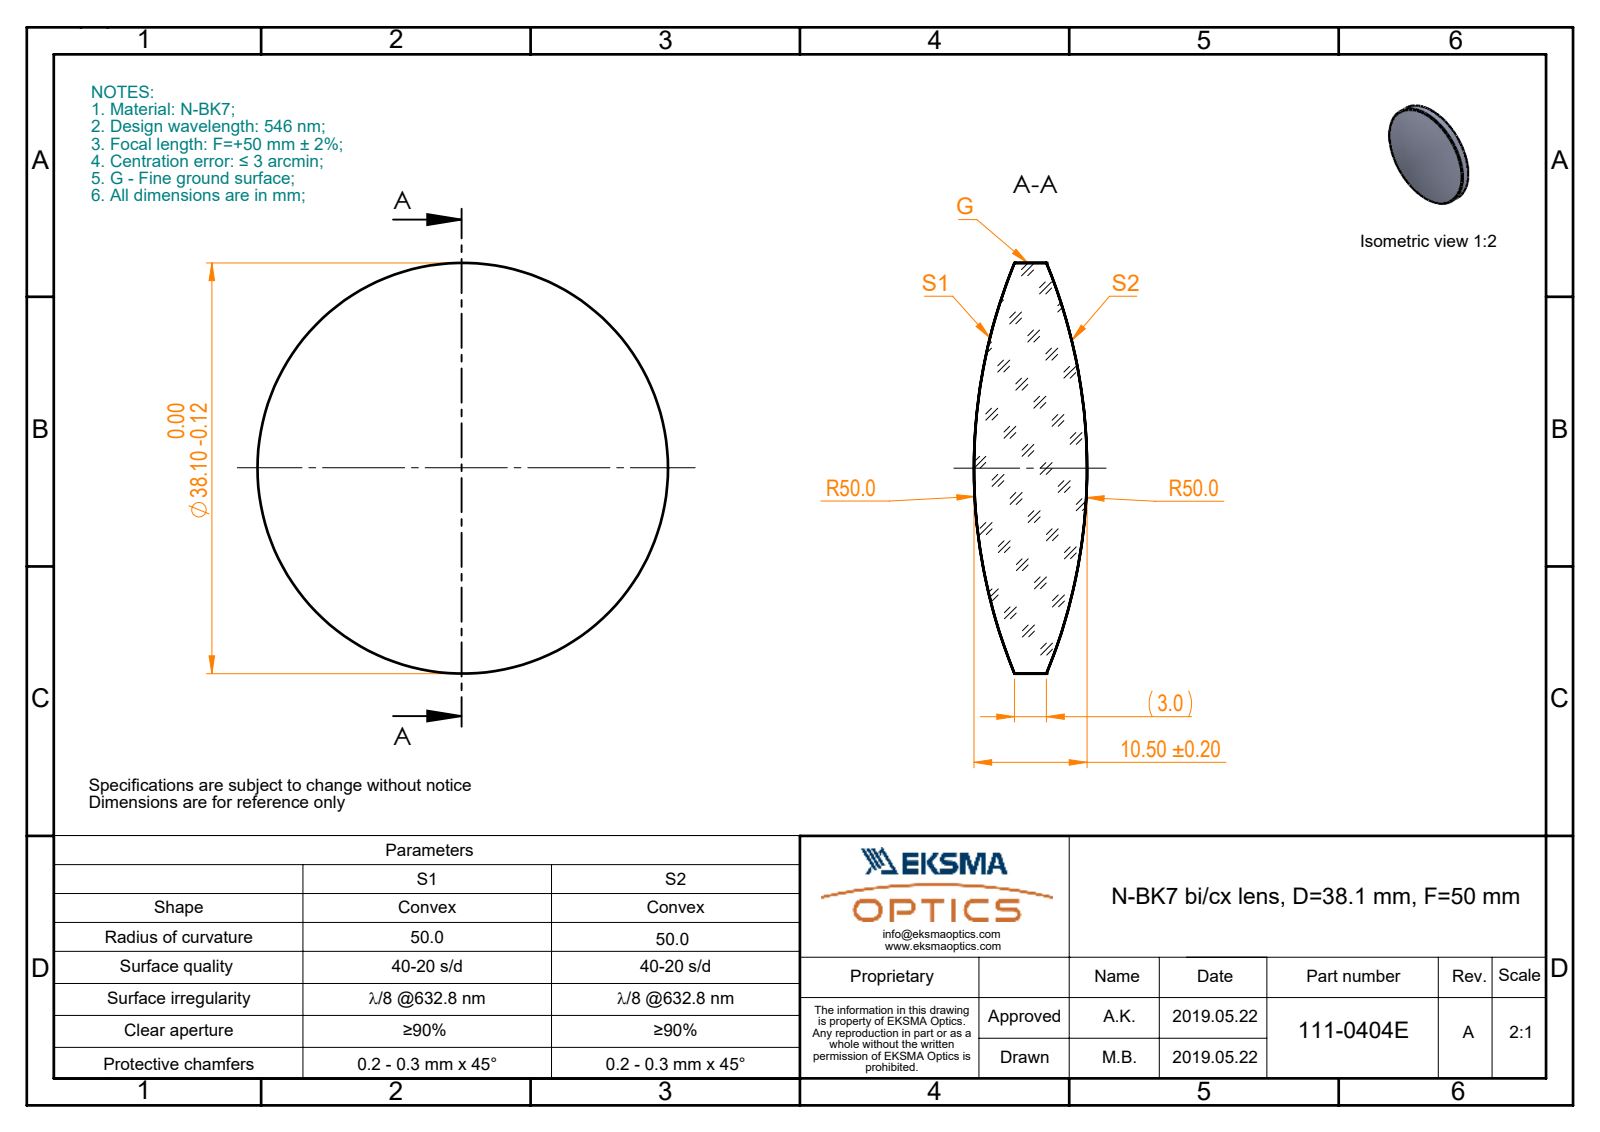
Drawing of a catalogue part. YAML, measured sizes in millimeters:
part_name: "111-0404E BK7 bi-cx 38.1 F50"
step_written_by: "SolidWorks 2017 (CONFIG_CONTROL_DESIGN)"
units: millimeters
bodies: {solids: 1, faces: 6, planar: 0, cylindrical: 2, other: 4}
overall_size: [38.1, 38.1, 10.5]
volume: 7728
surface_area: 2724
round_bosses_or_shafts:
  - {diameter: 38.1, count: 1}
